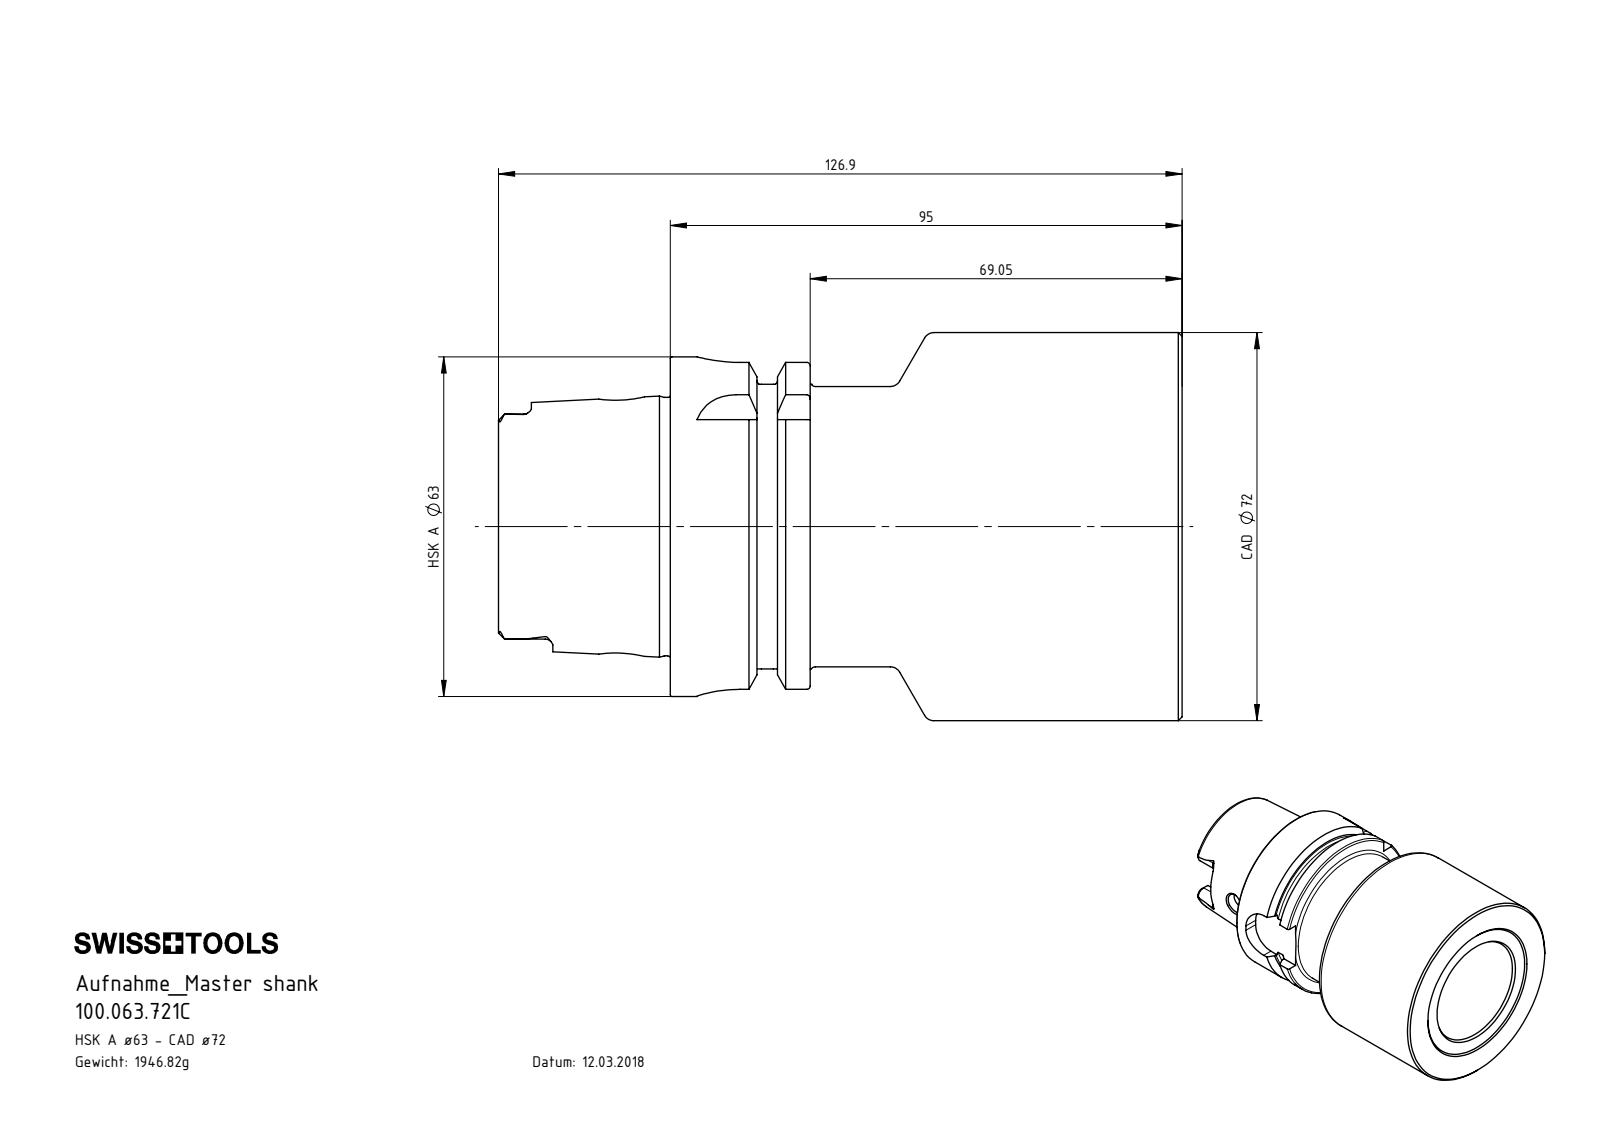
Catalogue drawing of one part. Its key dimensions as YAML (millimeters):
part_name: "100.063.721C"
step_written_by: "SolidWorks 2017 (CONFIG_CONTROL_DESIGN)"
units: millimeters
bodies: {solids: 1, faces: 202, planar: 50, cylindrical: 55, other: 97}
overall_size: [126.9, 72, 72]
volume: 248001
surface_area: 47646
round_holes:
  - {diameter: 7.5, count: 1}
  - {diameter: 8.4, count: 1}
  - {diameter: 10, count: 1}
  - {diameter: 17, count: 1}
  - {diameter: 19, count: 1}
  - {diameter: 32, count: 1}
  - {diameter: 34, count: 1}
  - {diameter: 36.5, count: 1}
  - {diameter: 40, count: 1}
  - {diameter: 40.6, count: 1}
round_bosses_or_shafts:
  - {diameter: 72, count: 1}
  - {diameter: 63, count: 1}
  - {diameter: 54.95, count: 1}
  - {diameter: 52, count: 1}
  - {diameter: 47.94, count: 1}
partial_cylinders:
  - {radius: 1.4, count: 6}
  - {radius: 2.88, count: 4}
  - {radius: 8, count: 4}
face_to_face_distances: [95, 25, 70, 94.4, 69.4, 0.6, 25.95, 0.95, 68.45, 69.05]
